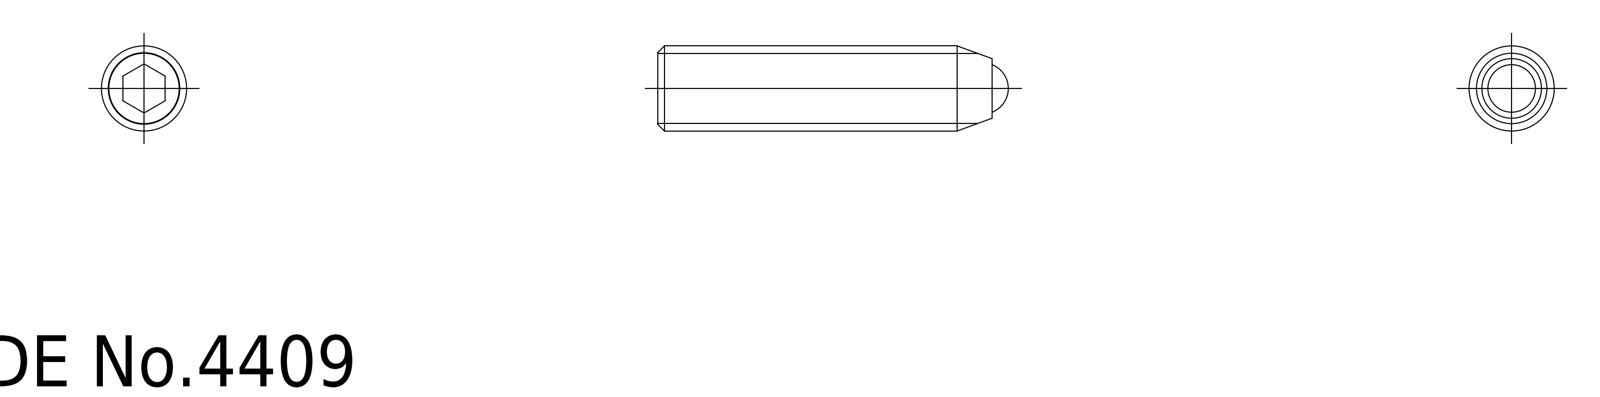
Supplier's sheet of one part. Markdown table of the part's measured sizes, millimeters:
| quantity | value |
| --- | --- |
| part name | ball; SCSS_M5_20_R_18903_36 |
| STEP written by | CADfix (AUTOMOTIVE_DESIGN) |
| units | millimeters |
| bodies | 2 solids, 20 faces (0 planar, 0 cylindrical, 20 other) |
| overall size | 20.6 × 5 × 5 |
| volume | 346 mm³ |
| surface area | 422 mm² |
